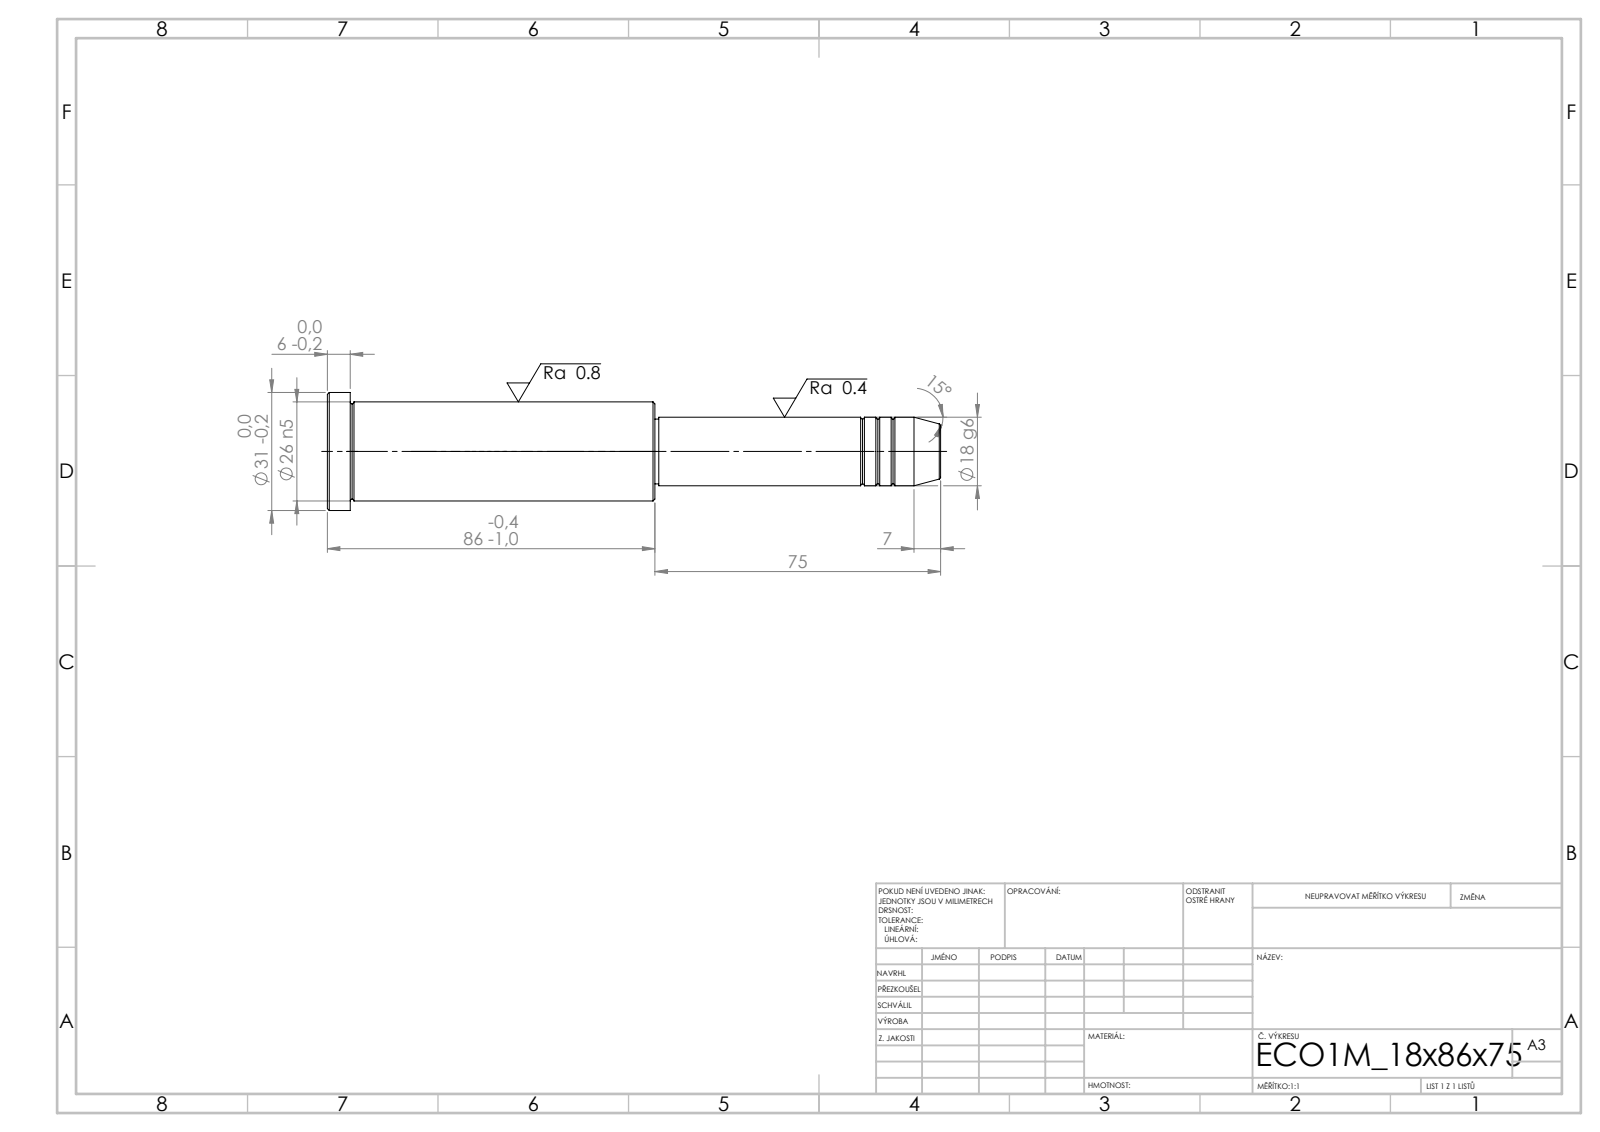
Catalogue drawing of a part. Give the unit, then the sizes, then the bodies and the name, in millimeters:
Units: millimetres
Overall size (bounding box): 161 × 31 × 31
Round bosses / shafts (diameter × count): ⌀31 ×1, ⌀26 ×1, ⌀18 ×1, ⌀17 ×1
Main face-to-face distances: 86, 80, 6, 75, 155, 161, 74, 1, 81, 87
Volume: 65 595 mm³ · Surface area: 12 870 mm²
Bodies: 1 solid, 43 faces (5 planar, 14 cylindrical, 24 other)
STEP written by: SolidWorks 2019 (CONFIG_CONTROL_DESIGN)
